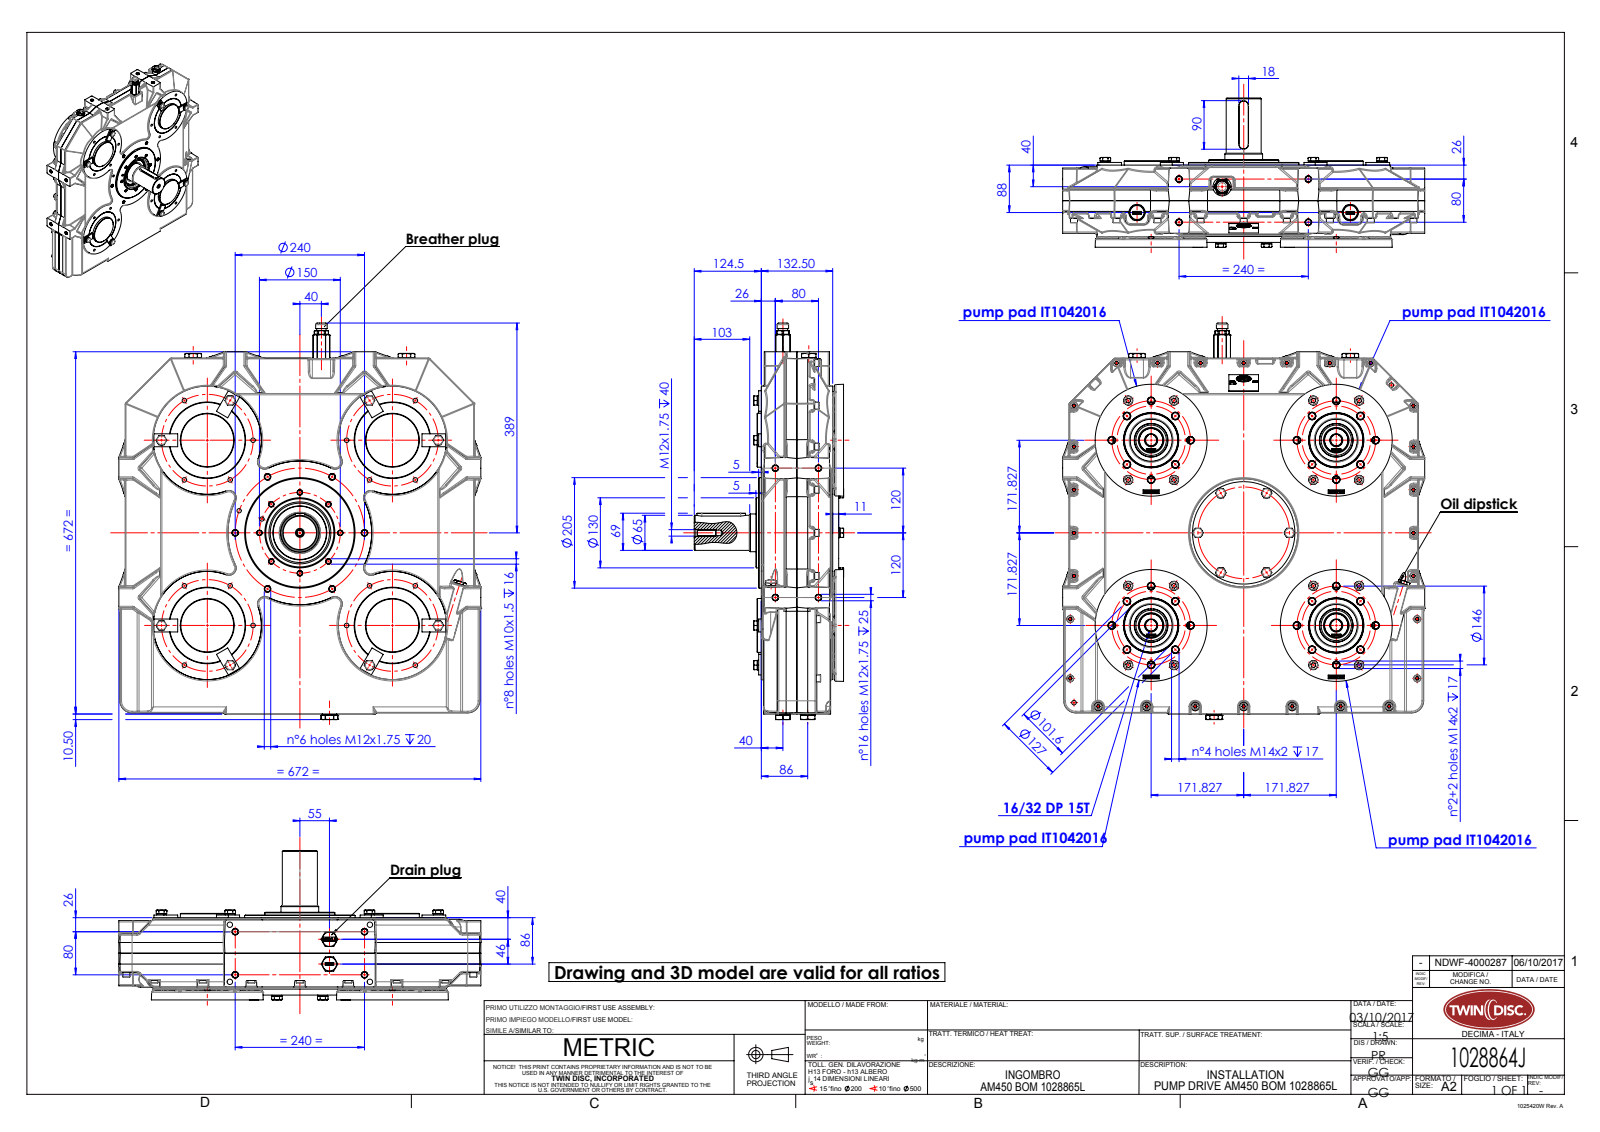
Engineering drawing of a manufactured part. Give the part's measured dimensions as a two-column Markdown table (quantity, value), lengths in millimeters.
| quantity | value |
| --- | --- |
| part name | IT4588040_rev00-installation; IT0000203_rev00-installation; IT0000394_rev00-installation; ITam230-018_rev00-installation (+7 more) |
| STEP written by | SolidWorks 2015 (AUTOMOTIVE_DESIGN) |
| units | millimeters |
| bodies | 78 solids, 8187 faces (3599 planar, 2031 cylindrical, 2557 other) |
| overall size | 735.8 × 672.41 × 277.2 |
| volume | 6 032 000 mm³ |
| surface area | 4 140 000 mm² |
| round holes (diameter × count) | 8.5 × 68, 12 × 48, 14 × 33, 10.2 × 29, 11 × 26, 17 × 16, 10 × 12, 16 × 7, 80 × 5, 100 × 5, 125 × 5, 20 × 4 |
| round bosses / shafts (diameter × count) | 13 × 28, 8 × 28, 10 × 26, 16 × 16, 16.2 × 15, 18.1 × 14, 140 × 5, 82 × 5 |
| partial cylindrical surfaces (radius × count) | 2.5 × 324, 2 × 106, 1.5 × 27, 3 × 24, 5 × 24, 10 × 6, 1 × 4, 28.5 × 4 |
| main face-to-face distances | 128.5, 4, 62.5, 66, 148.5, 124.5, 62, 66.5, 132.5, 20 |
| hole center spacings | 85, 120, 178.39, 243, 254.31, 57.4, 75, 106.89 |
